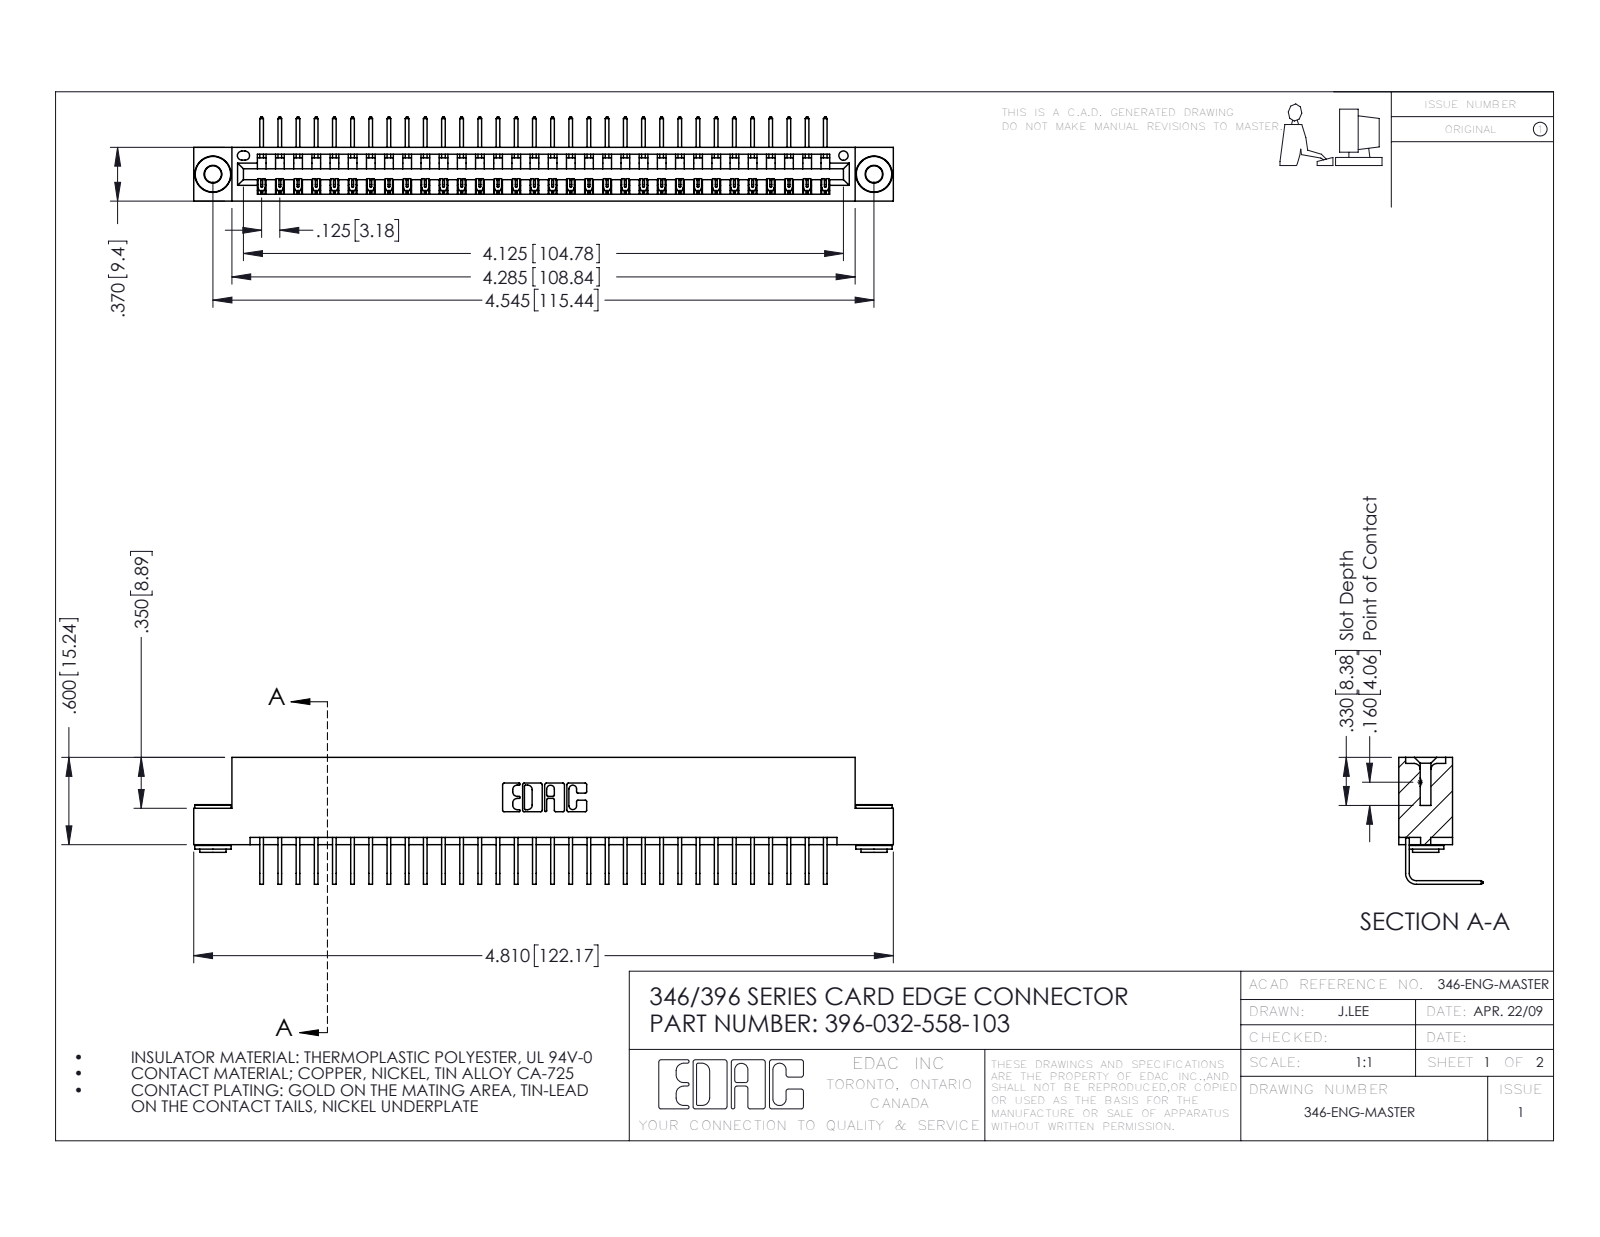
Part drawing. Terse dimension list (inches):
name: 345-250-002_345-250-002-102; 346 Part_Flush Mounting Lugs - 0.156 Dia-TH; 396-032-558-103; 345-292-001_558 Tail - 2
written by: SolidWorks 2016 (CONFIG_CONTROL_DESIGN)
unit: in
bodies: 35 solids, 2080 faces (1430 planar, 642 cylindrical, 8 other)
size: 4.81 × 0.873 × 0.58
volume: 0.717 in³; area: 23.93 in²
holes: 2× ⌀0.116, 2× ⌀0.156, 1× ⌀0.064
bosses: 2× ⌀0.25, 2× ⌀0.18, 2× ⌀0.136
rounds: 64× R0.006, 22× R0.01, 6× R0.007, 6× R0.031, 3× R0.026, 2× R0.031, 2× R0.04, 1× R0.014
face distances: 0.322, 0.048, 0.37, 0.25, 0.025, 0.298, 0.072, 0.148, 0.222, 0.1
hole spacings: 0.246, 4.337, 4.545
